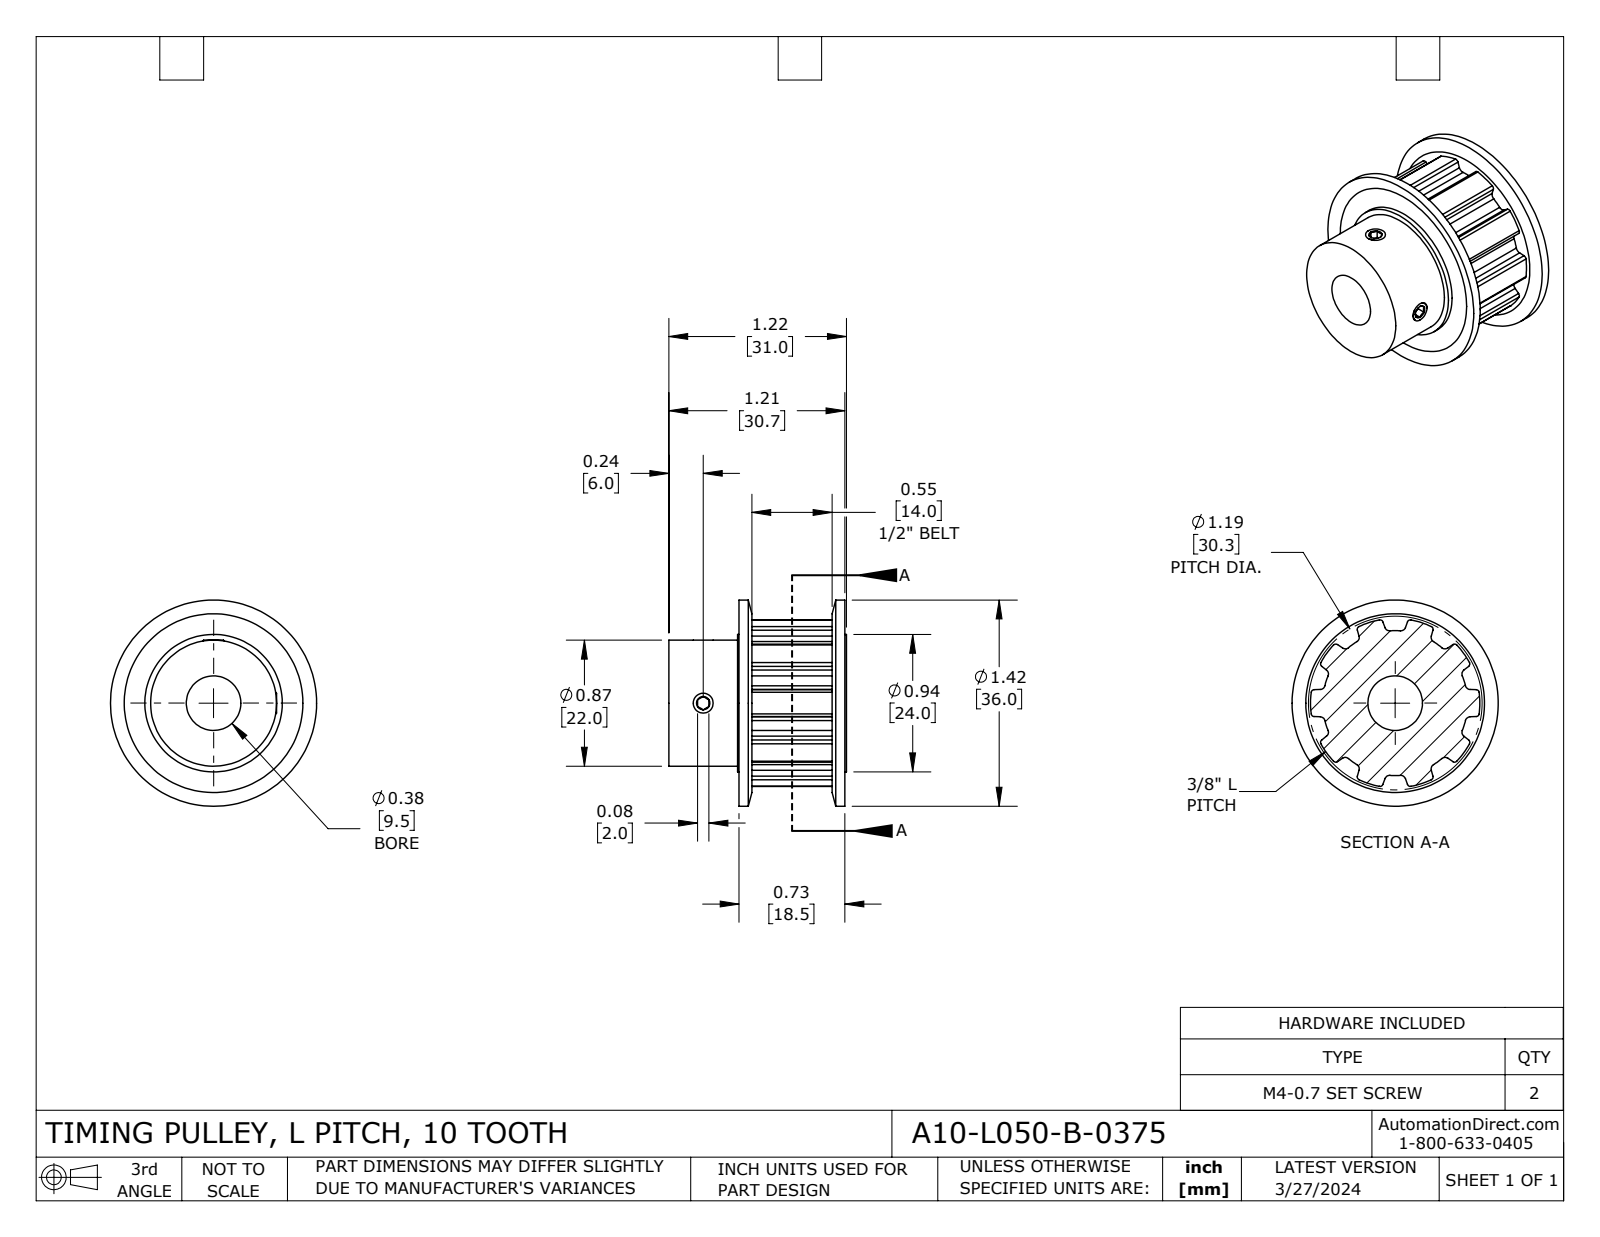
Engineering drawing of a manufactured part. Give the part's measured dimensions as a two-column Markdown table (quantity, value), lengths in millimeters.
| quantity | value |
| --- | --- |
| part name | A10-L050-B-0375 |
| STEP written by | SolidWorks 2021 (CONFIG_CONTROL_DESIGN) |
| units | millimeters |
| bodies | 5 solids, 172 faces (45 planar, 93 cylindrical, 34 other) |
| overall size | 36 × 36 × 31 |
| volume | 14 843 mm³ |
| surface area | 7 931 mm² |
| round holes (diameter × count) | 3.3 × 2, 9.53 × 1, 24 × 1 |
| round bosses / shafts (diameter × count) | 4 × 2, 36 × 1, 22 × 1 |
| partial cylindrical surfaces (radius × count) | 0.53 × 20, 0.86 × 20, 12.65 × 1, 14.78 × 1 |
| main face-to-face distances | 1.6, 15.6, 14, 2.5, 16.5, 0.9, 18.1, 17.2, 31, 30.1 |
